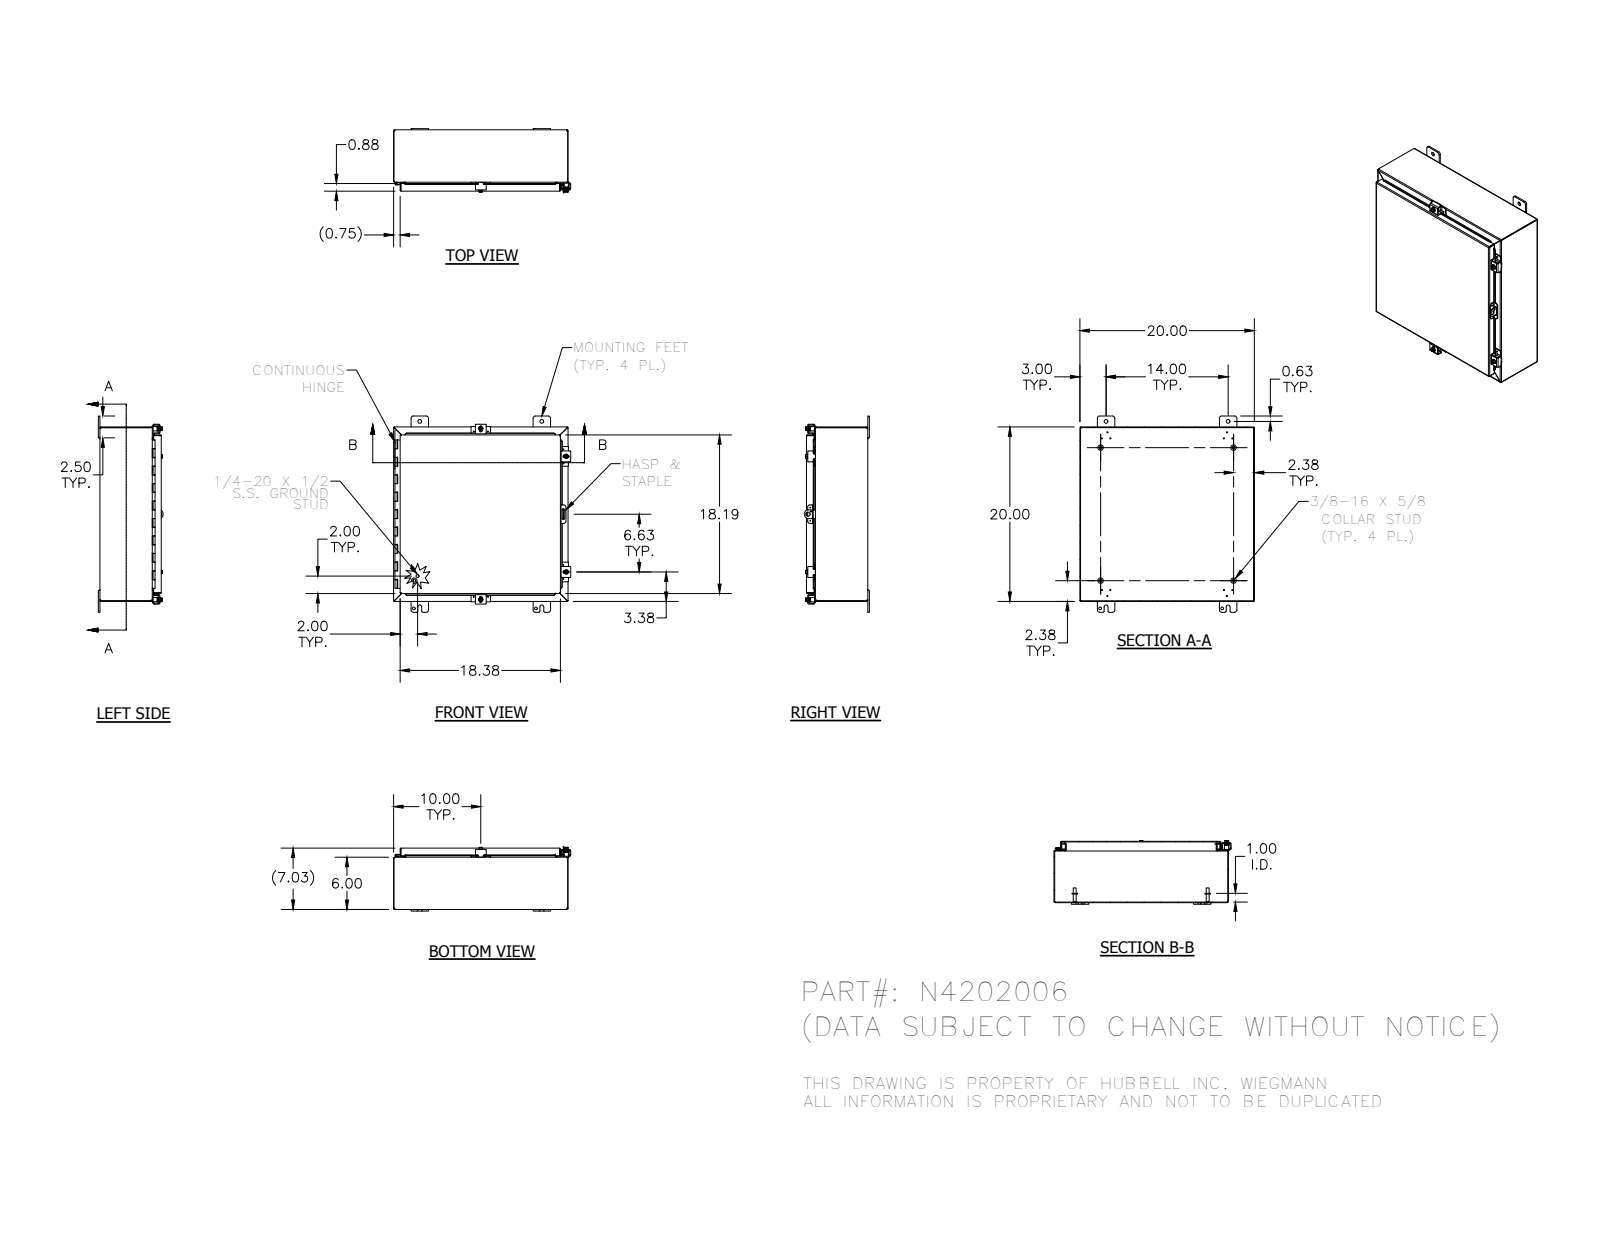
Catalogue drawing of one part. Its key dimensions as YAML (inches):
part_name: "388116_1; 328104P-1_1; 328104L_1; 328104T_1 (+8 more)"
step_written_by: "SolidWorks 2014 (AUTOMOTIVE_DESIGN)"
units: inches
bodies: {solids: 37, faces: 1614, planar: 633, cylindrical: 724, other: 257}
overall_size: [22.5, 20.311, 7.41]
volume: 122.4
surface_area: 3170
round_holes:
  - {diameter: 0.12, count: 12}
  - {diameter: 0.11, count: 11}
  - {diameter: 0.211, count: 4}
  - {diameter: 0.281, count: 4}
  - {diameter: 0.3, count: 4}
  - {diameter: 0.313, count: 4}
  - {diameter: 0.438, count: 4}
  - {diameter: 0.125, count: 1}
  - {diameter: 0.156, count: 1}
  - {diameter: 0.5, count: 1}
round_bosses_or_shafts:
  - {diameter: 0.25, count: 6}
  - {diameter: 0.625, count: 4}
  - {diameter: 0.52, count: 4}
  - {diameter: 0.5, count: 4}
  - {diameter: 0.35, count: 4}
  - {diameter: 0.33, count: 4}
  - {diameter: 0.115, count: 2}
  - {diameter: 0.337, count: 1}
partial_cylinders:
  - {radius: 0.03, count: 49}
  - {radius: 0.062, count: 33}
  - {radius: 0.125, count: 33}
  - {radius: 0.25, count: 29}
  - {radius: 0.031, count: 23}
  - {radius: 0.105, count: 23}
  - {radius: 0.07, count: 8}
  - {radius: 0.141, count: 8}
face_to_face_distances: [0.074, 6.959, 19.926, 6.885, 7.033, 19.852, 20, 5.926, 1.033, 6]
hole_center_spacings: [14, 0.876, 0.759, 0.839, 0.94, 0.969, 1.593, 1.995]
